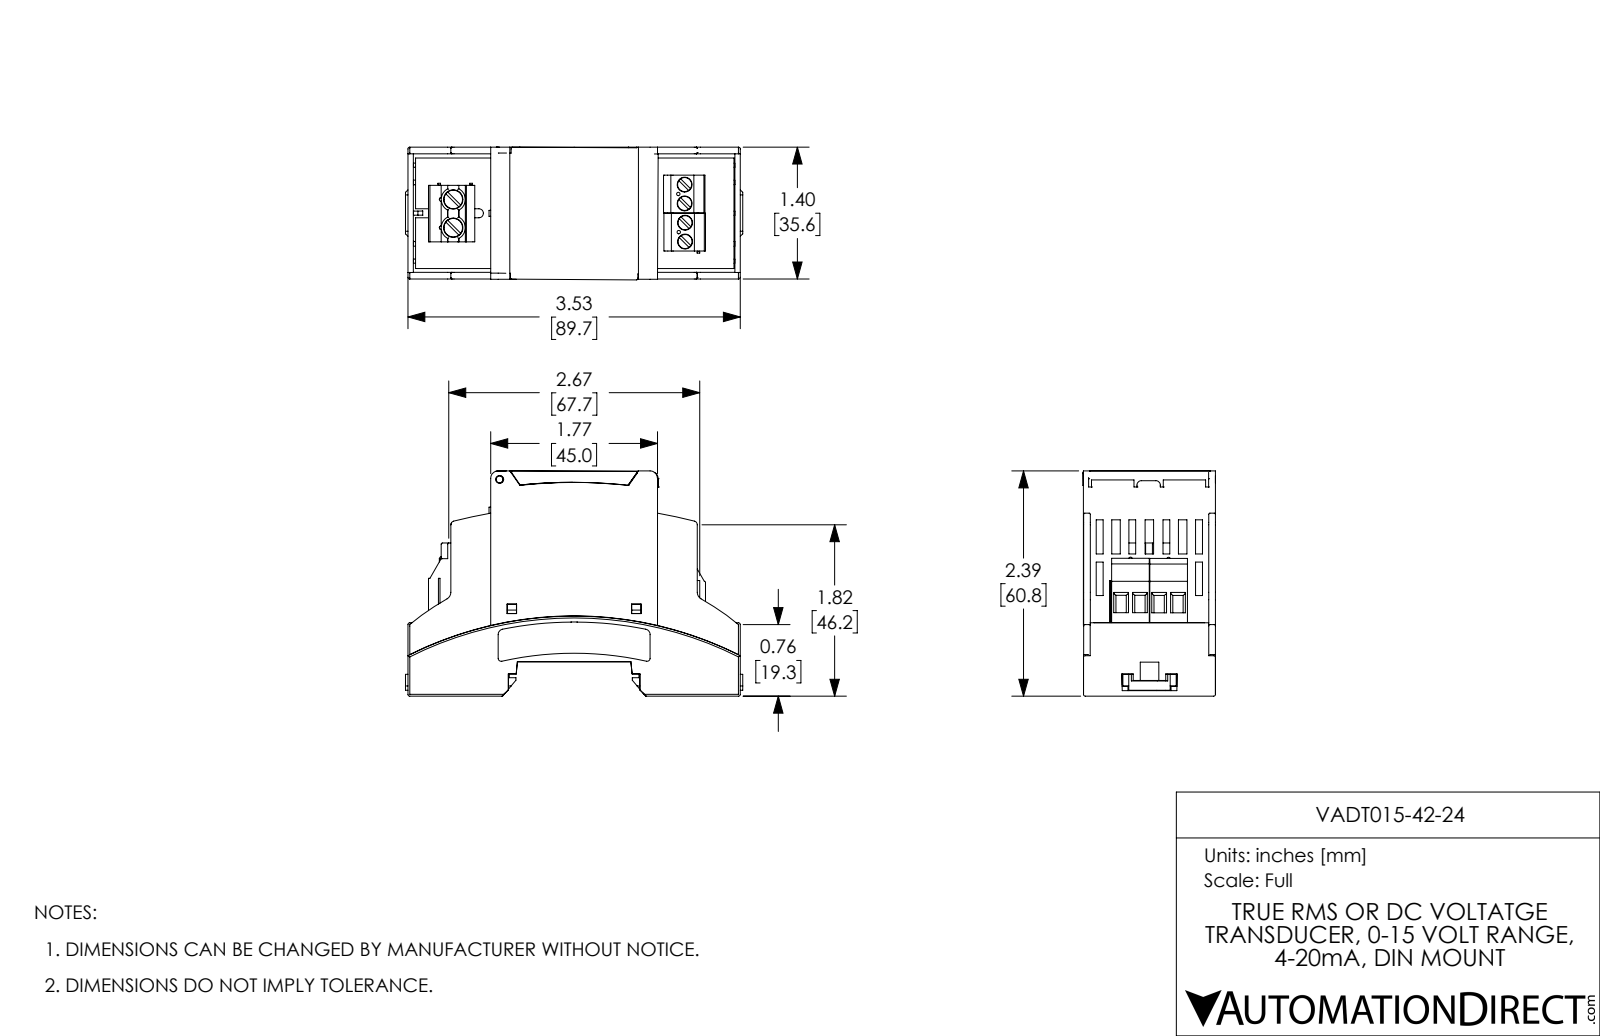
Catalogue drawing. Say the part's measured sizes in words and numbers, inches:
The part is named "VADT015-42-24". Its 3-D file was written by "SolidWorks 2021 (AUTOMOTIVE_DESIGN)". It is 7 solids with 895 faces: 538 planar, 166 cylindrical and 191 other. Overall it measures 4.203 by 2.279 by 1.435 inches. Its volume is 3.182 cubic inches and its surface area 78.38 square inches. Round holes: 4 of diameter 0.157, 2 of diameter 0.205. Round bosses or shafts: 6 of diameter 0.051, 4 of diameter 0.15, 2 of diameter 0.197, 2 of diameter 0.018. Partial cylindrical surfaces (rounded edges, fillets, slot ends): 20 of radius 0.006, 12 of radius 0.039, 11 of radius 0.02, 8 of radius 0.008, 8 of radius 0.026, 4 of radius 0.012, 4 of radius 0.032, 4 of radius 0.04. The main face-to-face distances are 1.435, 0.064, 0.501, 0.437, 0.266, 0.702, 0.767, 1.279, 1.249, 1.129. The hole center spacings are 0.2, 0.4, 2.467, 0.375, 0.6, 2.468, 2.468, 2.482.
